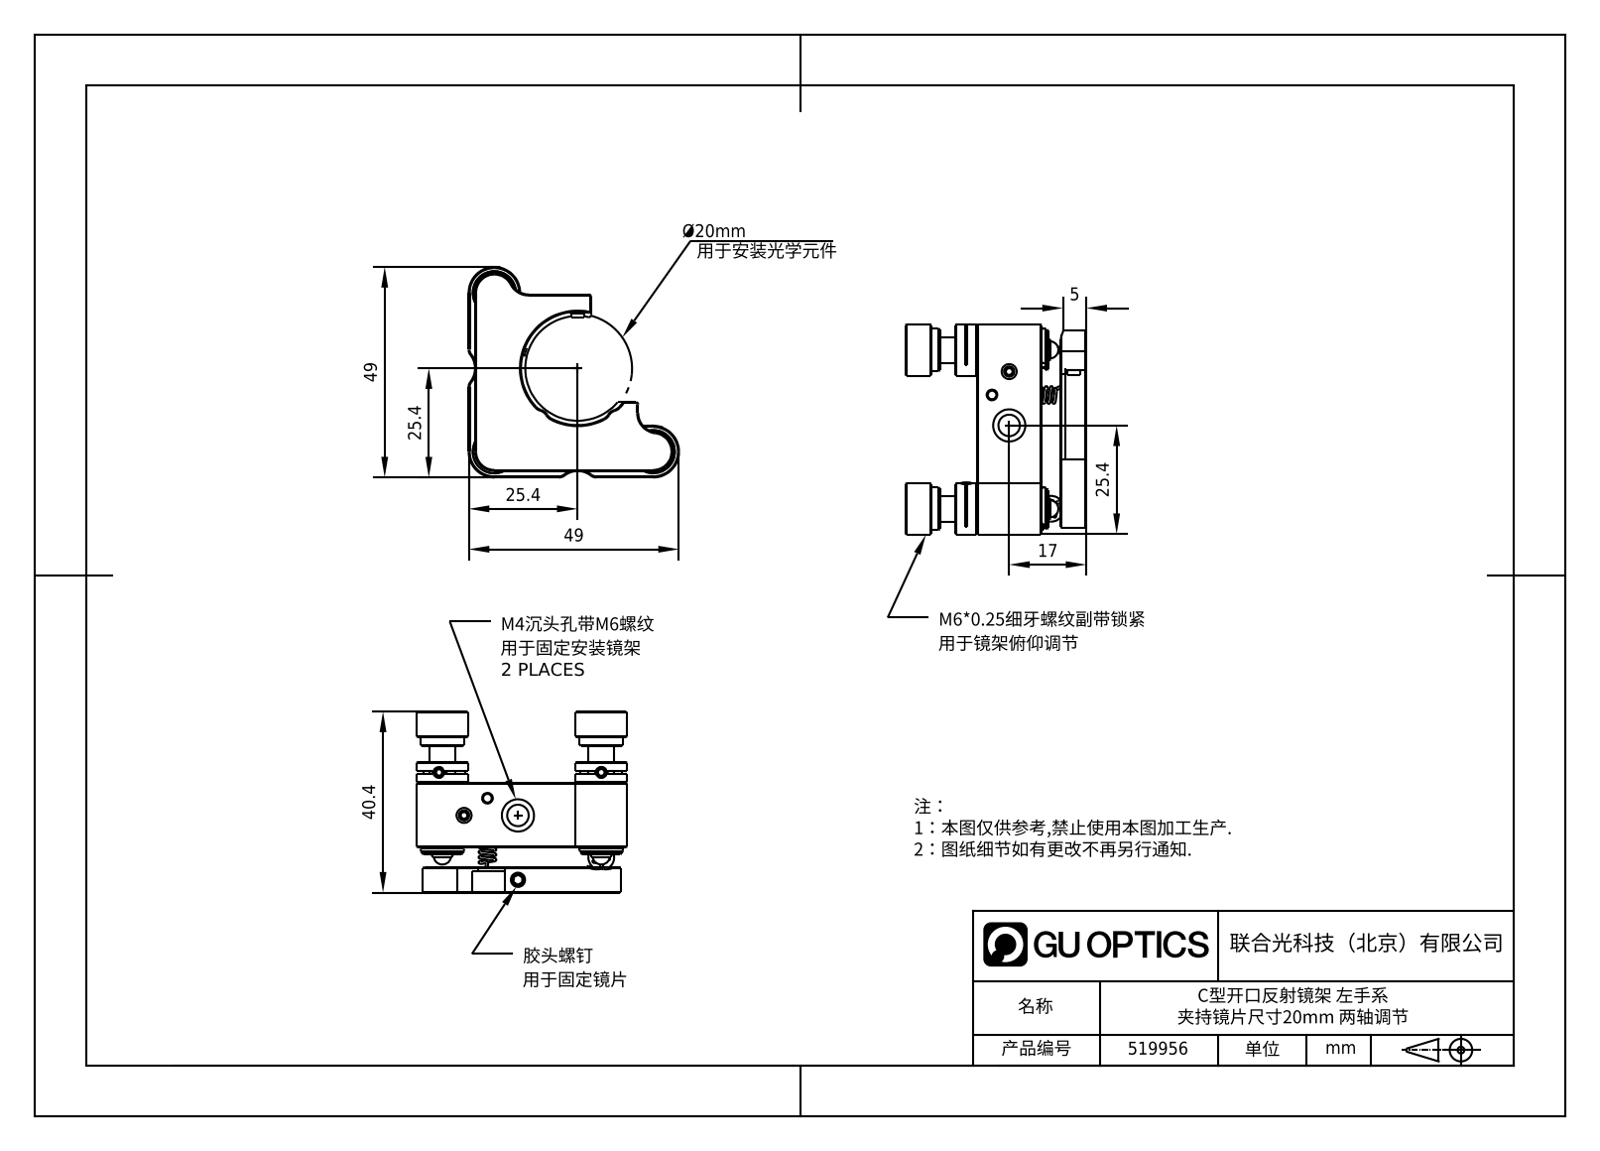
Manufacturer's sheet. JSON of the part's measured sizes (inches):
{"part_name": "JC版，2.1.13.21，OMC-20L-2，20mmC型开口反射调整架，左手，2轴", "step_written_by": "SolidWorks 2022 (AUTOMOTIVE_DESIGN)", "units": "inches", "bodies": {"solids": 0, "faces": 1019, "planar": 460, "cylindrical": 331, "other": 228}, "overall_size": [2.028, 2.028, 1.602], "round_holes": [[0.098, 4], [0.236, 4], [0.157, 2], [0.181, 2], [0.197, 2], [0.315, 2], [0.13, 1], [0.378, 1]], "round_bosses_or_shafts": [[0.118, 8], [0.059, 4], [0.157, 3], [0.492, 2], [0.472, 2], [0.413, 2], [0.374, 2], [0.315, 2]], "partial_cylinders_radius": [[0.031, 8], [0.039, 8], [0.012, 7], [0.098, 5], [0.02, 4], [0.049, 4], [0.207, 3], [0.006, 2]], "face_to_face_distances": [0.236, 0.965, 0.728, 0.138, 0.374, 0.591, 0.039, 0.089, 0.108, 0.453], "hole_center_spacings": [0.197, 0.384, 0.65, 1.033, 1.128, 1.493, 1.781, 0.283]}
